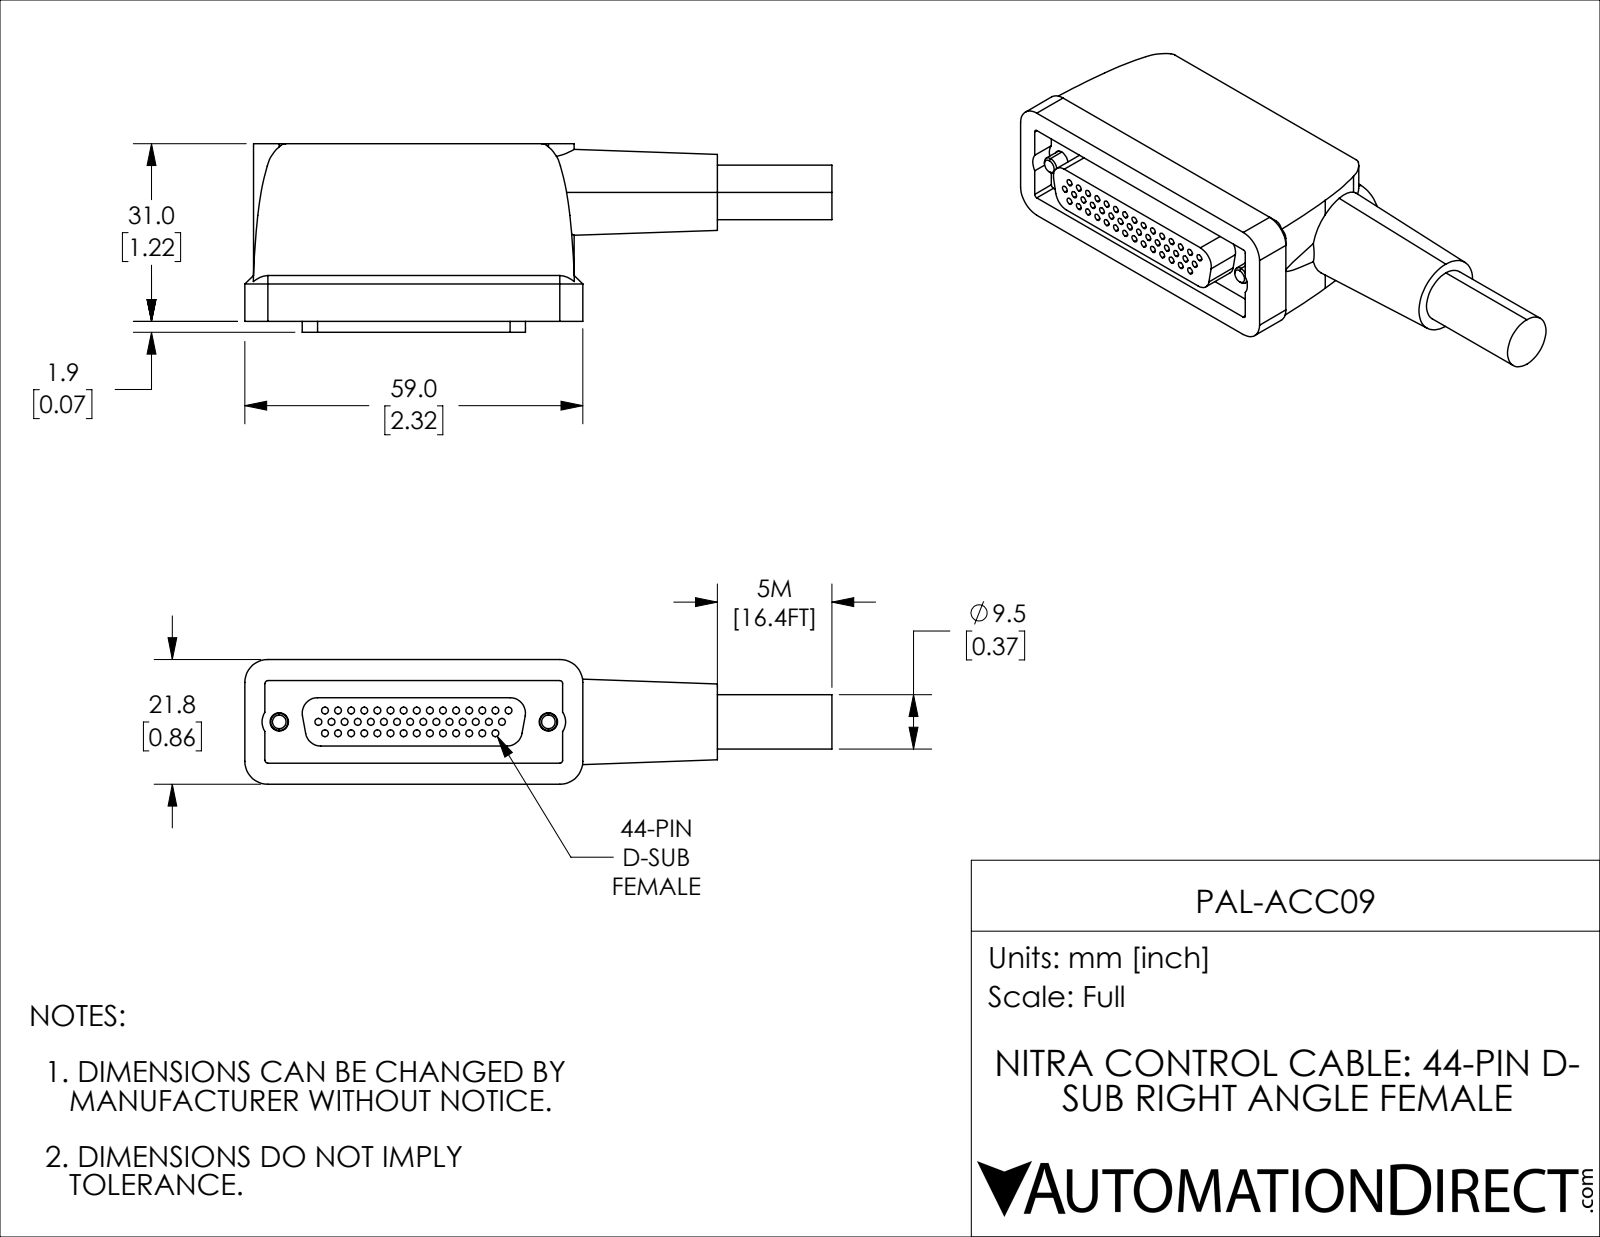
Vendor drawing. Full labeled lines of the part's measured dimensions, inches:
Part name (STEP PRODUCT): PAL-ACC09
STEP written by: SolidWorks 2019 (CONFIG_CONTROL_DESIGN)
Units: inches
Bodies: 1 solid, 243 faces (90 planar, 139 cylindrical, 14 other)
Overall size (bounding box): 4.035 × 1.295 × 0.858
Volume: 2.283 in³ · Surface area: 18.47 in²
Round holes (diameter × count): ⌀0.047 ×44, ⌀0.126 ×2, ⌀0.197 ×2
Round bosses / shafts (diameter × count): ⌀0.181 ×2, ⌀0.118 ×2, ⌀0.374 ×1
Partial cylindrical surfaces — rounded edges, fillets, slot ends (radius × count): R0.02 ×4, R0.106 ×4, R0.157 ×4, R0.055 ×2, R0.118 ×2, R0.177 ×2, R0.256 ×2, R1.969 ×2
Main face-to-face distances: 0.74, 0.059, 0.799, 1.22, 0.161, 1.059, 0.146, 0.713, 0.087, 0.654
Hole centre spacings: 0.09, 0.238, 0.156, 0.18, 0.27, 0.09, 0.156, 0.18
